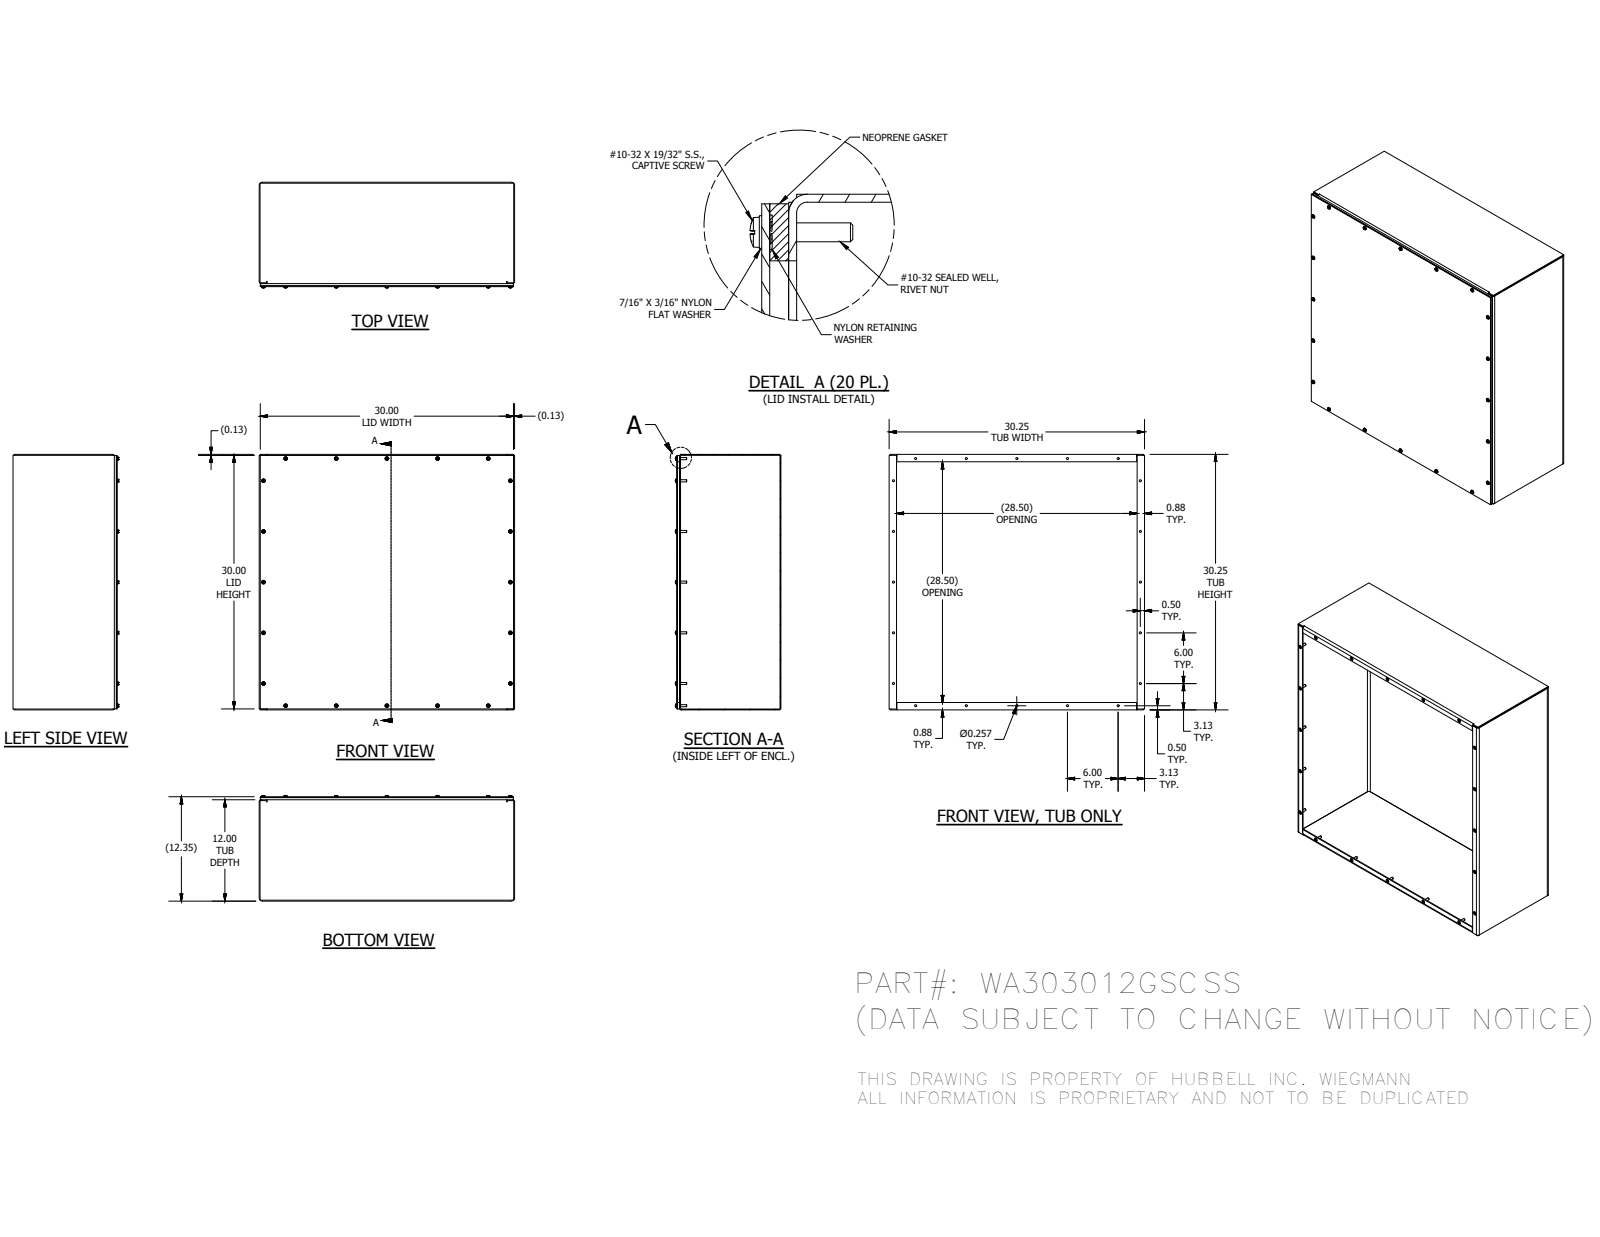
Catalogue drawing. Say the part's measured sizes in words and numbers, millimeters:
The part is named "WA303012GSCSSBLR; WA3012GSCSSTB; WA3030GSCSSLID; WA3030GSCSSSTRIPGSK (+5 more)". Its 3-D file was written by "Autodesk Inventor 2016 (AUTOMOTIVE_DESIGN)". It is 85 solids with 1698 faces: 958 planar, 320 cylindrical and 420 other. Overall it measures 768.35 by 768.35 by 317.72 millimeters. Its volume is 6 018 000 cubic millimeters and its surface area 4 487 000 square millimeters. Round holes: 20 of diameter 3.96, 20 of diameter 4.78, 20 of diameter 4.98, 20 of diameter 6.53, 20 of diameter 7.06, 20 of diameter 7.14. Round bosses or shafts: 20 of diameter 11.51, 20 of diameter 11.11, 20 of diameter 10.31, 20 of diameter 6.3, 20 of diameter 4.25. Partial cylindrical surfaces (rounded edges, fillets, slot ends): 20 of radius 2.27, 4 of radius 0.79, 4 of radius 3.57, 4 of radius 6.21, 2 of radius 0.4, 2 of radius 6.35, 2 of radius 8.99. The main face-to-face distances are 2.64, 311.15, 765.7, 308.51, 313.79, 763.06, 768.34, 765.71, 2.65, 768.35. The hole center spacings are 152.4, 304.8, 457.2, 758.41, 431.26, 758.42, 679.55, 710.87.
